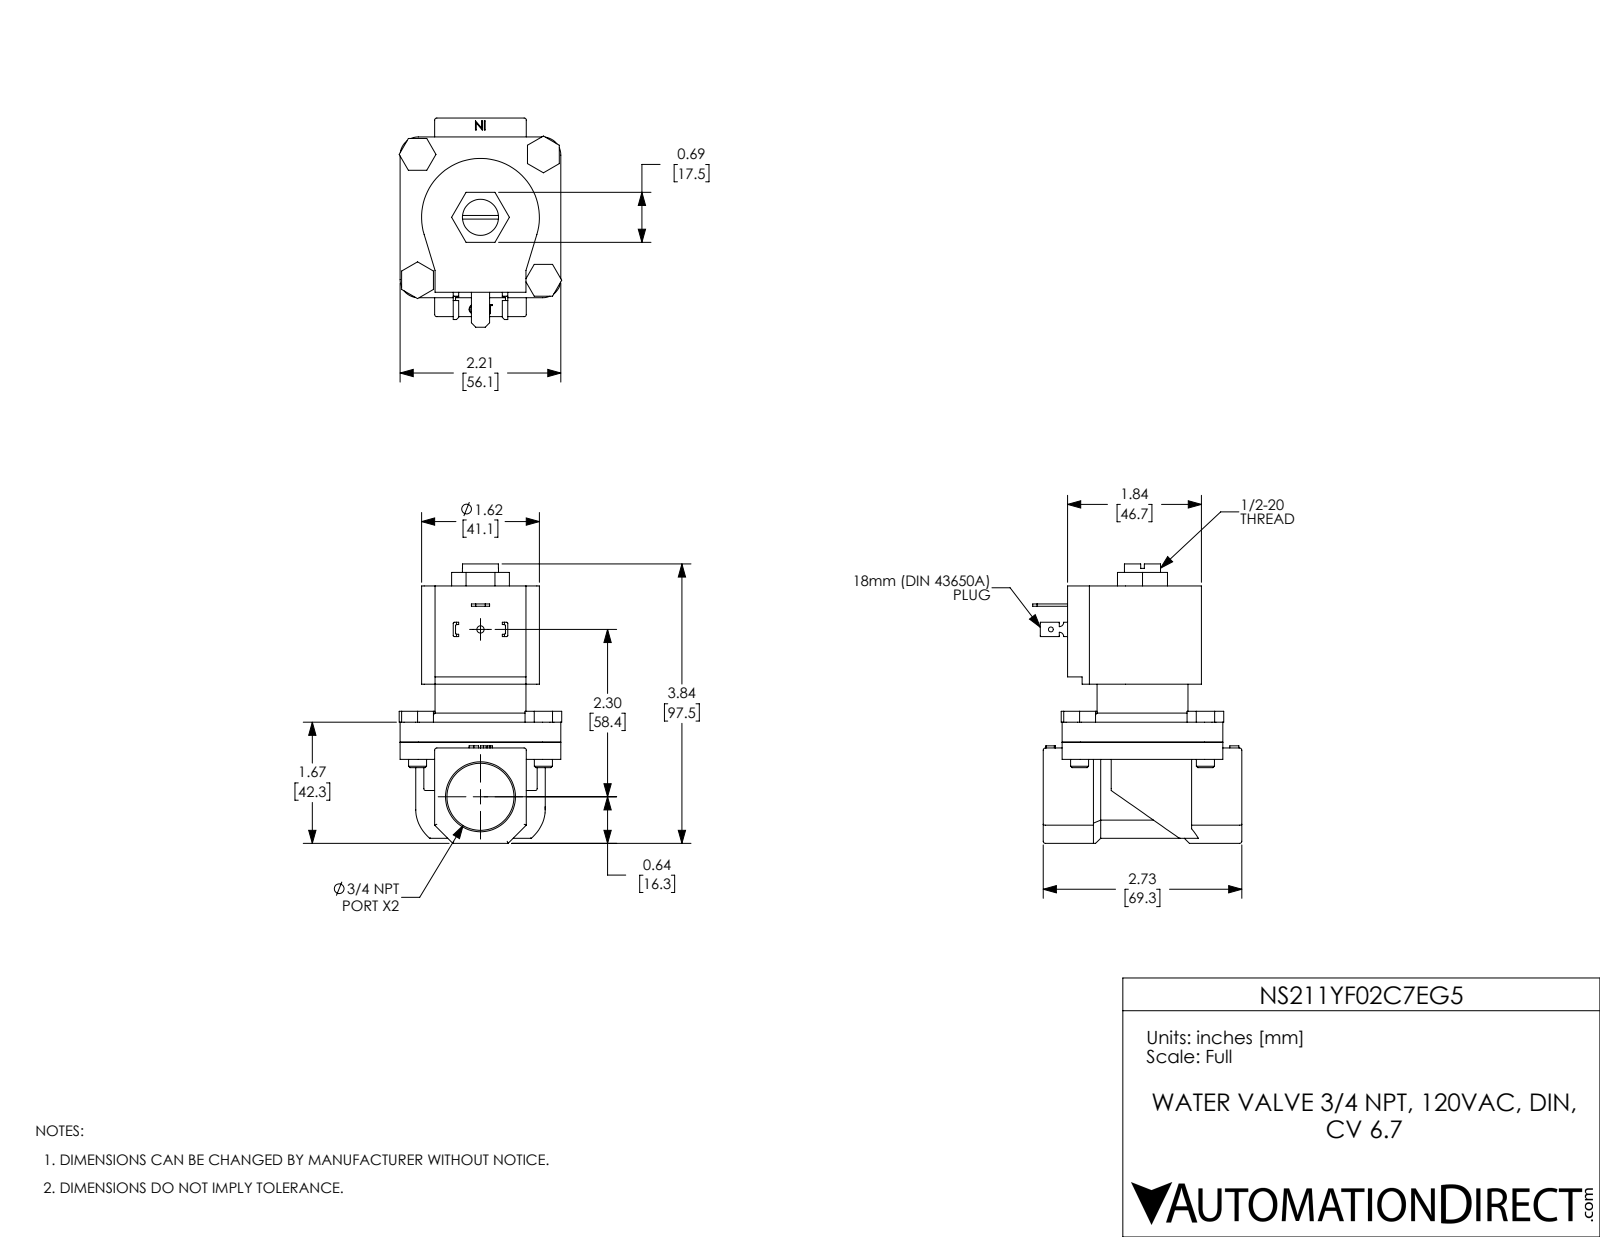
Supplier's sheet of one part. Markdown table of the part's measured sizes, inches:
| quantity | value |
| --- | --- |
| part name | NS211YF02C7EG5 |
| STEP written by | SolidWorks 2021 (CONFIG_CONTROL_DESIGN) |
| units | inches |
| bodies | 11 solids, 332 faces (198 planar, 99 cylindrical, 35 other) |
| overall size | 3.84 × 2.875 × 2.235 |
| volume | 9.853 in³ |
| surface area | 64.15 in² |
| round holes (diameter × count) | 0.25 × 4, 0.067 × 1, 0.1 × 1, 0.496 × 1, 0.512 × 1, 0.922 × 1, 1.155 × 1 |
| round bosses / shafts (diameter × count) | 0.248 × 4, 1.25 × 1 |
| partial cylindrical surfaces (radius × count) | 0.03 × 15, 0.015 × 8, 0.25 × 4, 0.06 × 2, 0.81 × 1, 0.89 × 1 |
| main face-to-face distances | 0.275, 2.148, 1.873, 0.475, 1.735, 2.21, 0.798, 0.523, 1.35, 0.236 |
| hole center spacings | 1.223, 1.73, 2.446, 2.3 |
